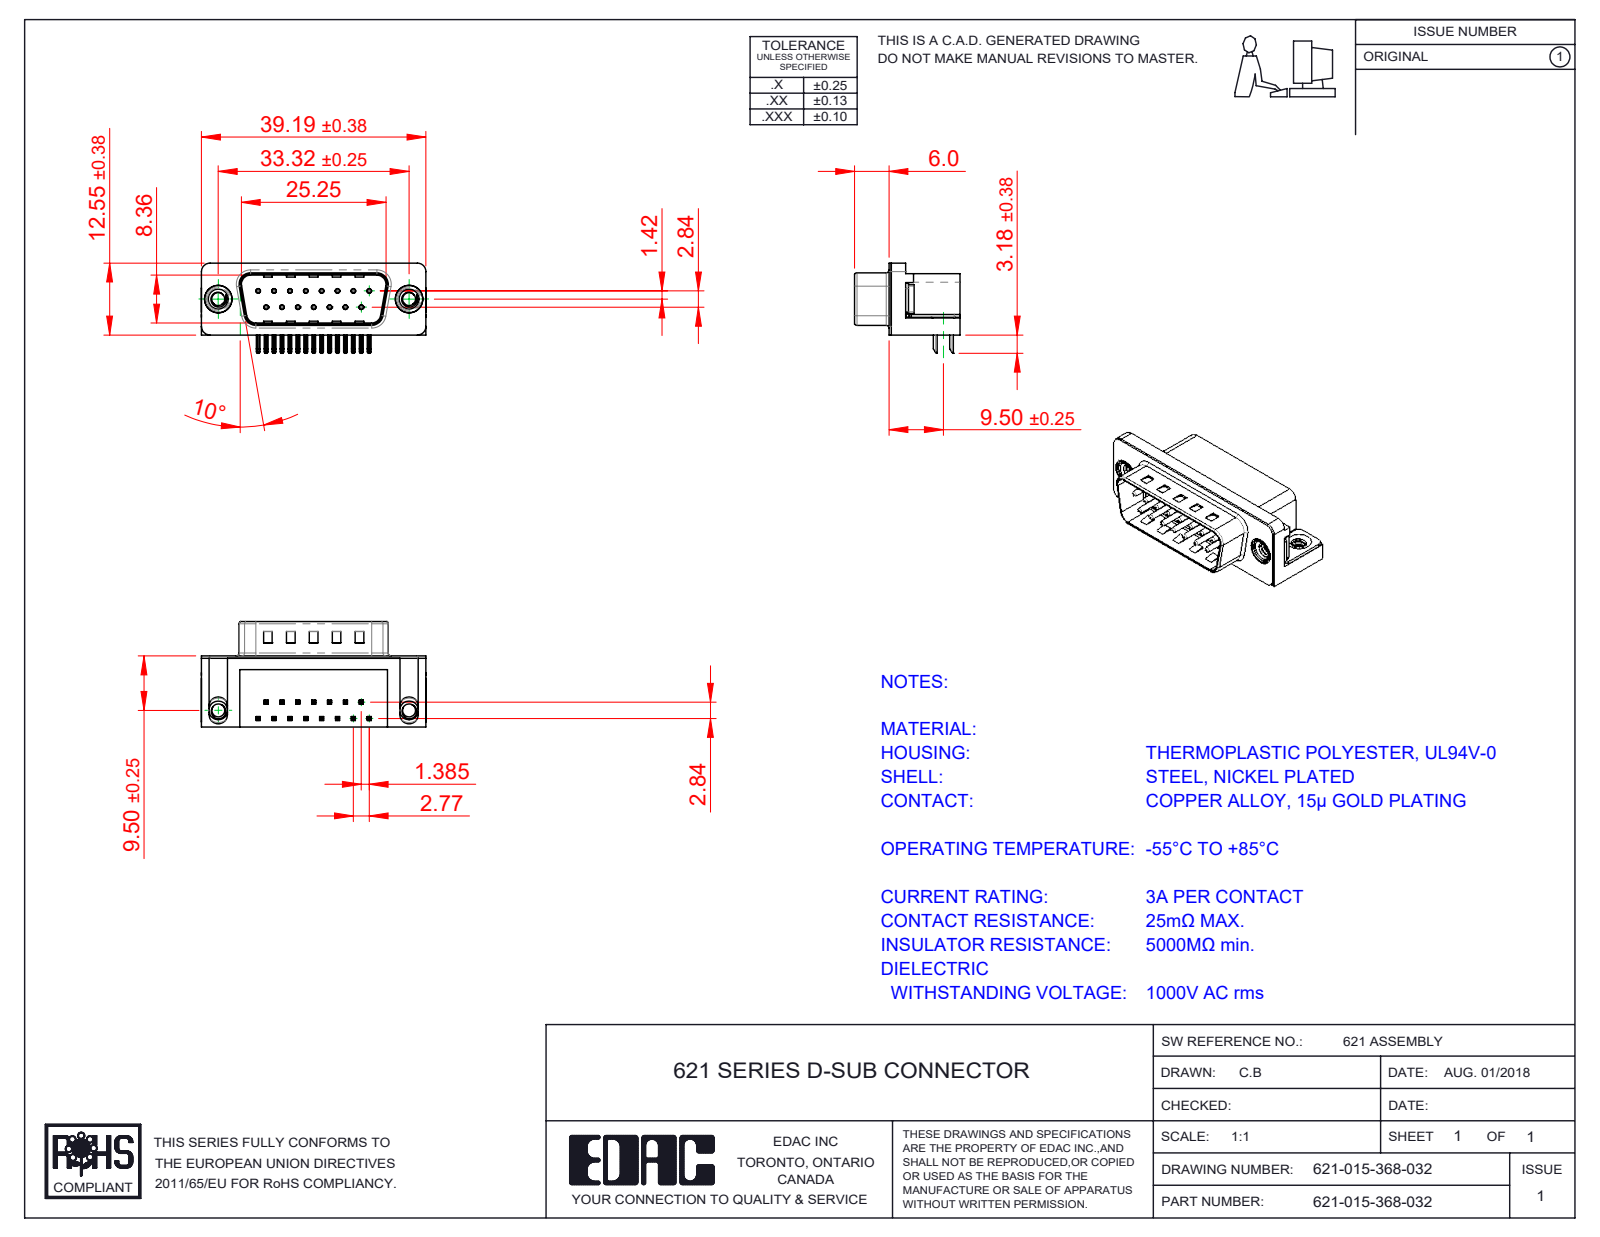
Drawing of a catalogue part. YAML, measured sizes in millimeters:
part_name: "621 Shell_15 Socket; 621 Housing_15 Socket; 621 4-40 Threaded Rivet; 621 2 Prong Board Lock (+3 more)"
step_written_by: "SolidWorks 2016 (CONFIG_CONTROL_DESIGN)"
units: millimeters
bodies: {solids: 21, faces: 1517, planar: 925, cylindrical: 453, other: 139}
overall_size: [39.22, 18.4, 16.25]
volume: 4415
surface_area: 5656
round_holes:
  - {diameter: 0.35, count: 15}
  - {diameter: 0.8, count: 15}
  - {diameter: 2.26, count: 2}
  - {diameter: 4, count: 2}
  - {diameter: 4.8, count: 2}
  - {diameter: 5, count: 2}
round_bosses_or_shafts:
  - {diameter: 0.75, count: 15}
  - {diameter: 4.9, count: 2}
  - {diameter: 4.75, count: 2}
  - {diameter: 3.9, count: 2}
partial_cylinders:
  - {radius: 0.25, count: 68}
  - {radius: 0.12, count: 30}
  - {radius: 1, count: 16}
  - {radius: 0.5, count: 14}
  - {radius: 1.6, count: 8}
  - {radius: 1.5, count: 6}
  - {radius: 0.32, count: 4}
  - {radius: 0.9, count: 4}
face_to_face_distances: [0.4, 12, 10.35, 2.1, 10.46, 12.4, 1.7, 10.86, 8.76, 9.5]
hole_center_spacings: [3.16, 2.77, 5.54, 8.31, 11.08, 5.03, 5.04, 7.48]
